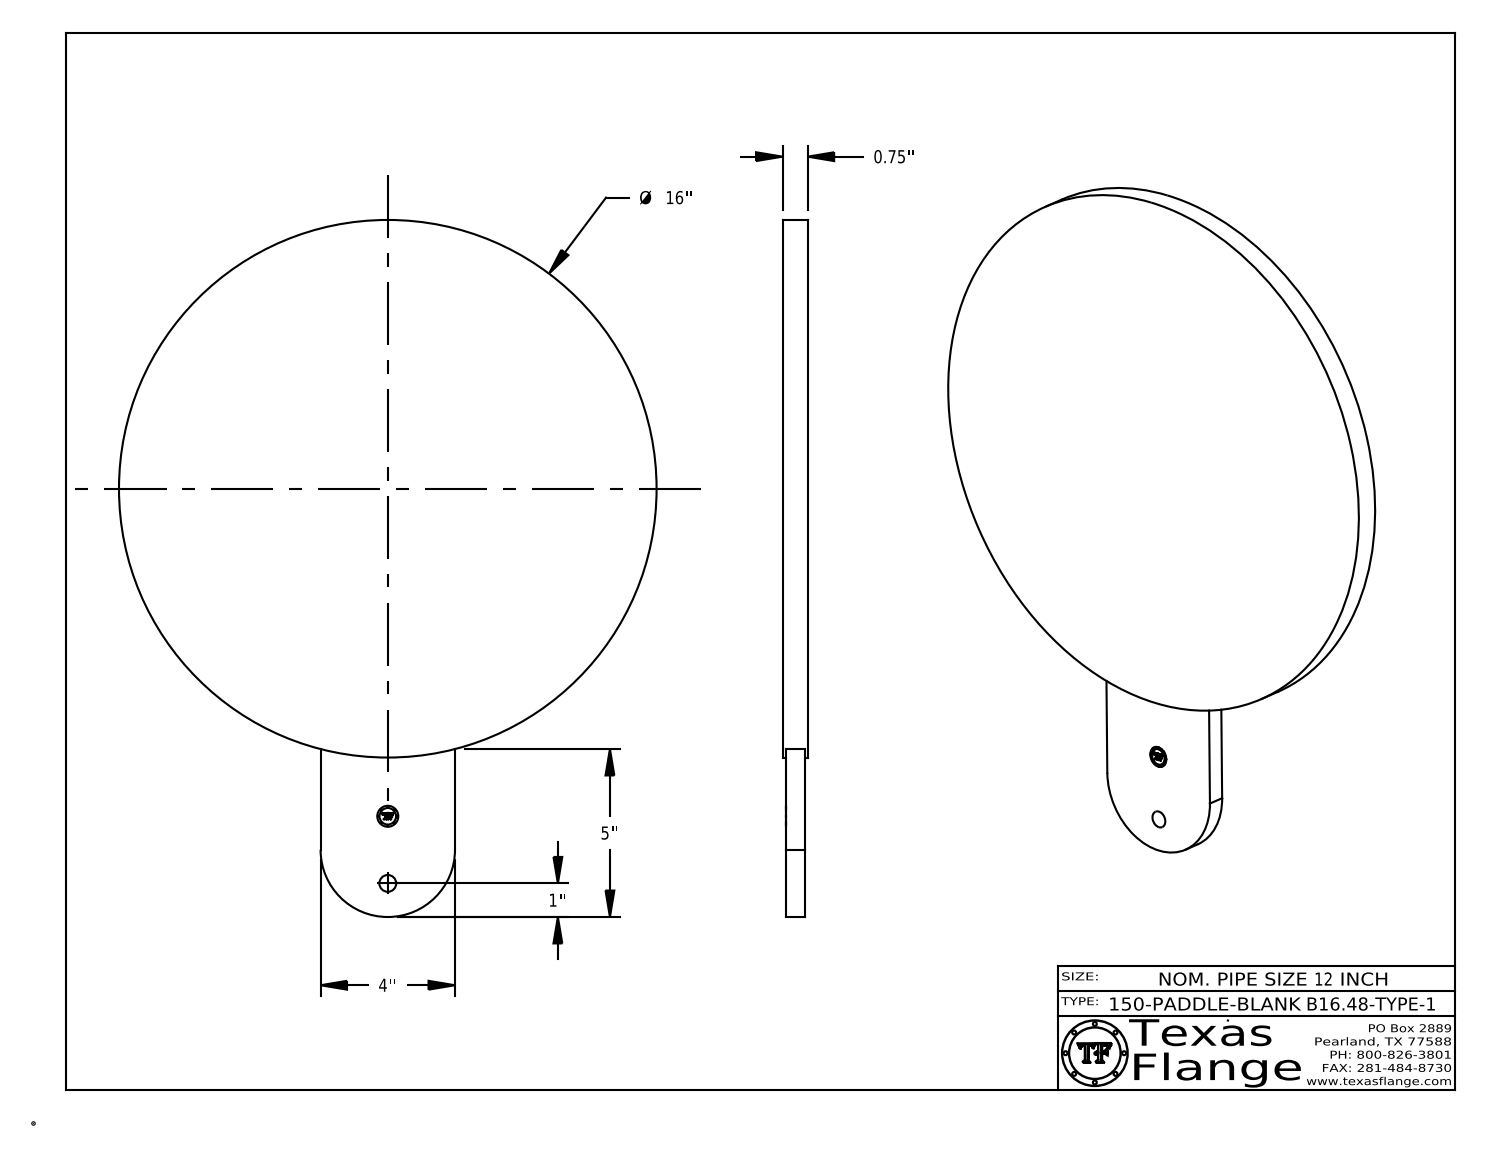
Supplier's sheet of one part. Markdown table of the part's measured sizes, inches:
| quantity | value |
| --- | --- |
| part name | 12-150-PADDLE-BLANK-B16.48-TYPE-1 |
| STEP written by | CATIA V5 STEP AP214 (AUTOMOTIVE_DESIGN) |
| units | inches |
| bodies | 1 solid, 396 faces (371 planar, 25 cylindrical, 0 other) |
| overall size | 20.746 × 16 × 0.75 |
| volume | 160.6 in³ |
| surface area | 480.3 in² |
| round holes (diameter × count) | 0.5 × 1, 0.625 × 1 |
| round bosses / shafts (diameter × count) | 0.038 × 8, 16 × 1, 0.492 × 1 |
| partial cylindrical surfaces (radius × count) | 2 × 1 |
| main face-to-face distances | 0.75, 0.094, 0.656, 0.562, 4, 0.641, 0.547, 0.015, 0.109, 1.937 |
| hole center spacings | 1.998 |
